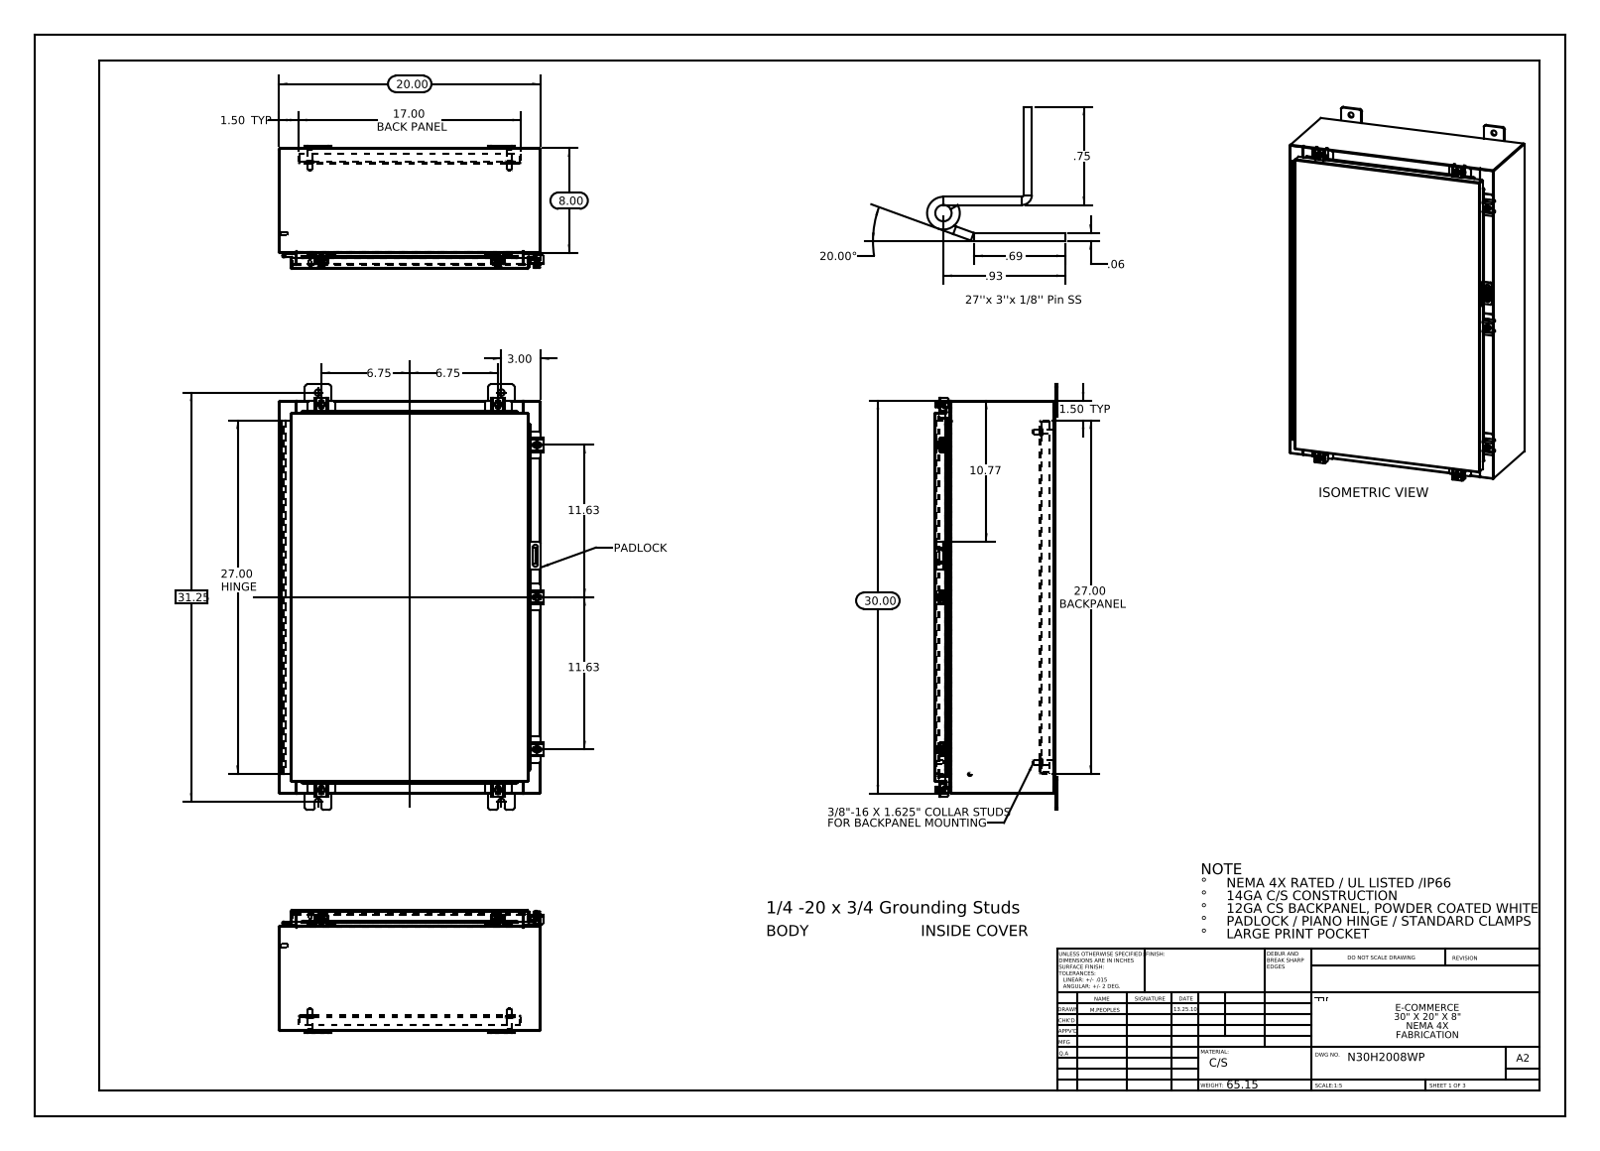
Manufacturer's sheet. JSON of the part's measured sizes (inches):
{"part_name": "N30H2008SSWP Padlock Staple; N30H2008SSWP Body; N30H2008SSWP Hinge Enclosure Side2; N30H2008SSWP Padlock Hasp (+8 more)", "step_written_by": "SolidWorks 2013 (CONFIG_CONTROL_DESIGN)", "units": "inches", "bodies": {"solids": 54, "faces": 2016, "planar": 1062, "cylindrical": 838, "other": 116}, "overall_size": [32.5, 20.211, 9.389], "volume_in3": 229.1, "surface_area_in2": 5747, "round_holes": [[0.5, 8], [0.213, 7], [0.26, 7], [0.125, 2]], "round_bosses_or_shafts": [[0.25, 8], [0.5, 7], [0.399, 7], [0.625, 4], [0.375, 4], [0.33, 4], [0.315, 2], [0.236, 2]], "partial_cylinders_radius": [[0.06, 34], [0.013, 27], [0.19, 24], [0.088, 21], [0.12, 14], [0.141, 14], [0.05, 11], [0.08, 10]], "face_to_face_distances": [0.075, 9.126, 9.051, 9.201, 0.104, 19.925, 1, 1.075, 8.051, 8.126], "hole_center_spacings": [27.365, 30.898, 0.431, 0.934, 1.858, 2.275, 2.276, 2.327]}
